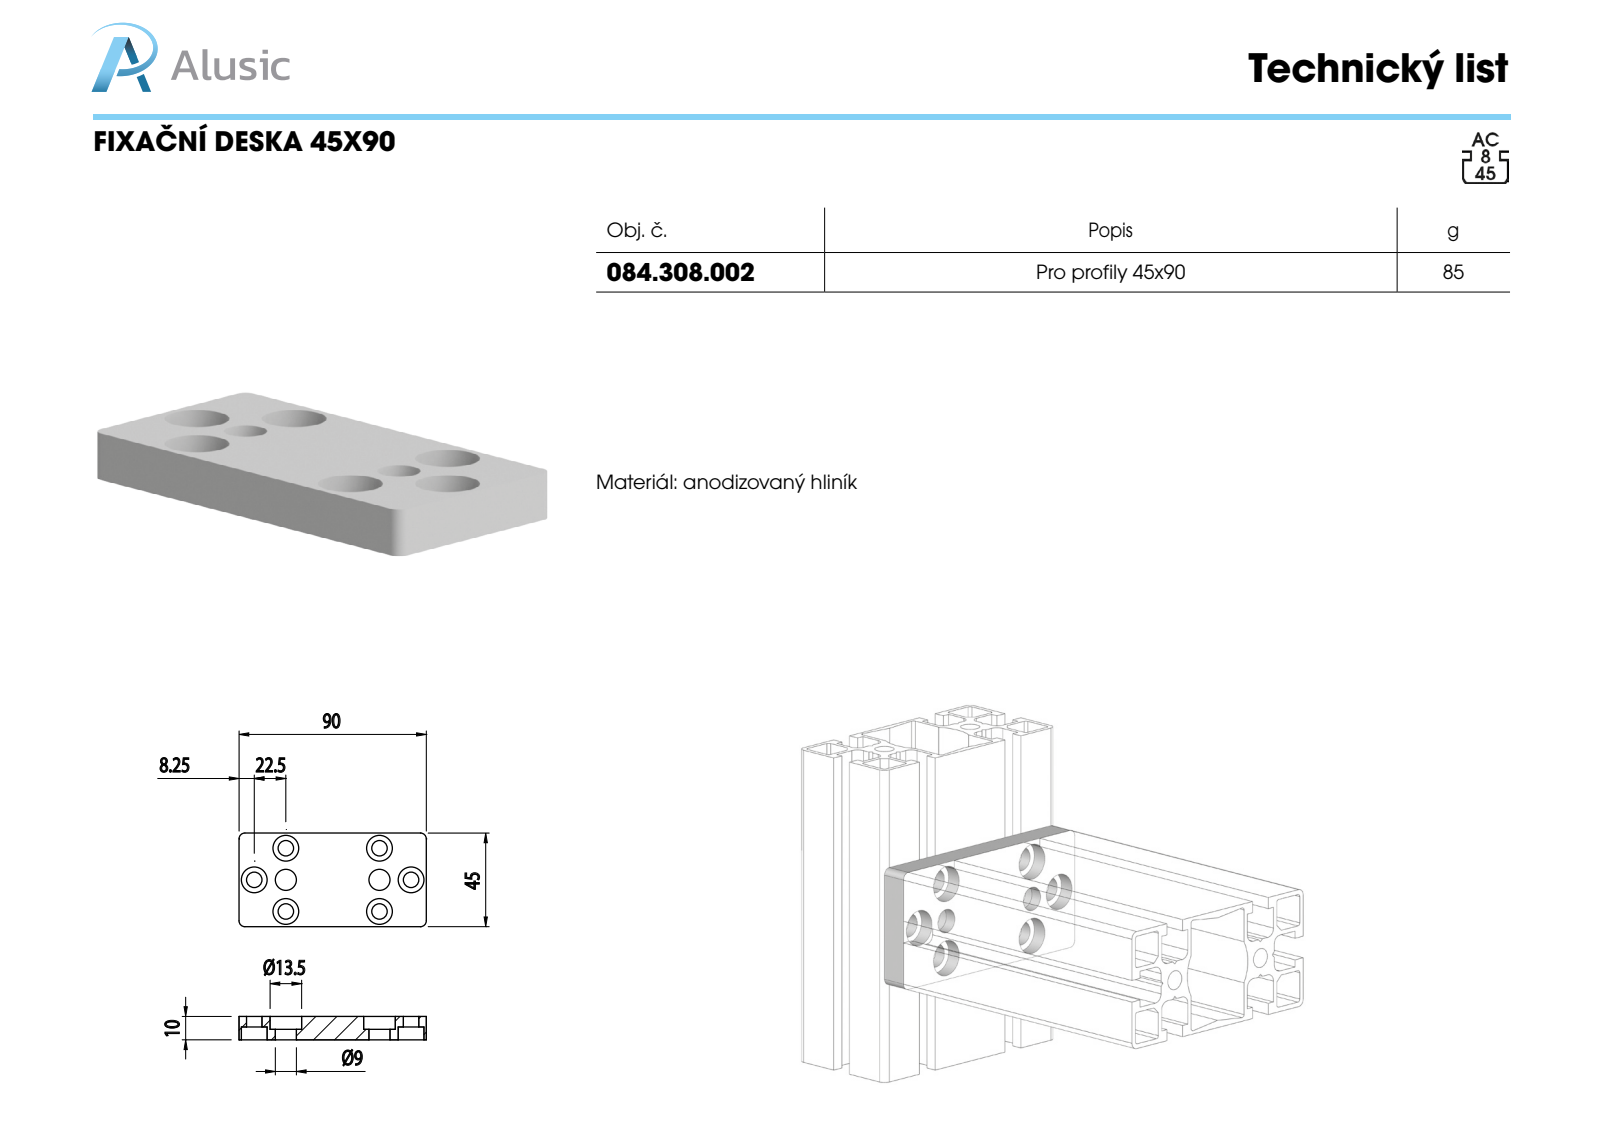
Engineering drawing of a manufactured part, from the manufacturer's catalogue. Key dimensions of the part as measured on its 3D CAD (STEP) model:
Part name (STEP PRODUCT): 084.308.002
STEP written by: SolidWorks 2011 (CONFIG_CONTROL_DESIGN)
Units: millimetres
Bodies: 1 solid, 50 faces (14 planar, 36 cylindrical, 0 other)
Overall size (bounding box): 90 × 45 × 10
Volume: 31 858 mm³ · Surface area: 12 612 mm²
Round holes (diameter × count): ⌀9 ×8, ⌀13.5 ×8
Partial cylindrical surfaces — rounded edges, fillets, slot ends (radius × count): R2.5 ×4
Main face-to-face distances: 10, 45, 4.5, 5.5, 90, 1
Hole centre spacings: 14.25, 20.15, 47.2, 60.94, 45, 28.5, 53.27, 59.25
